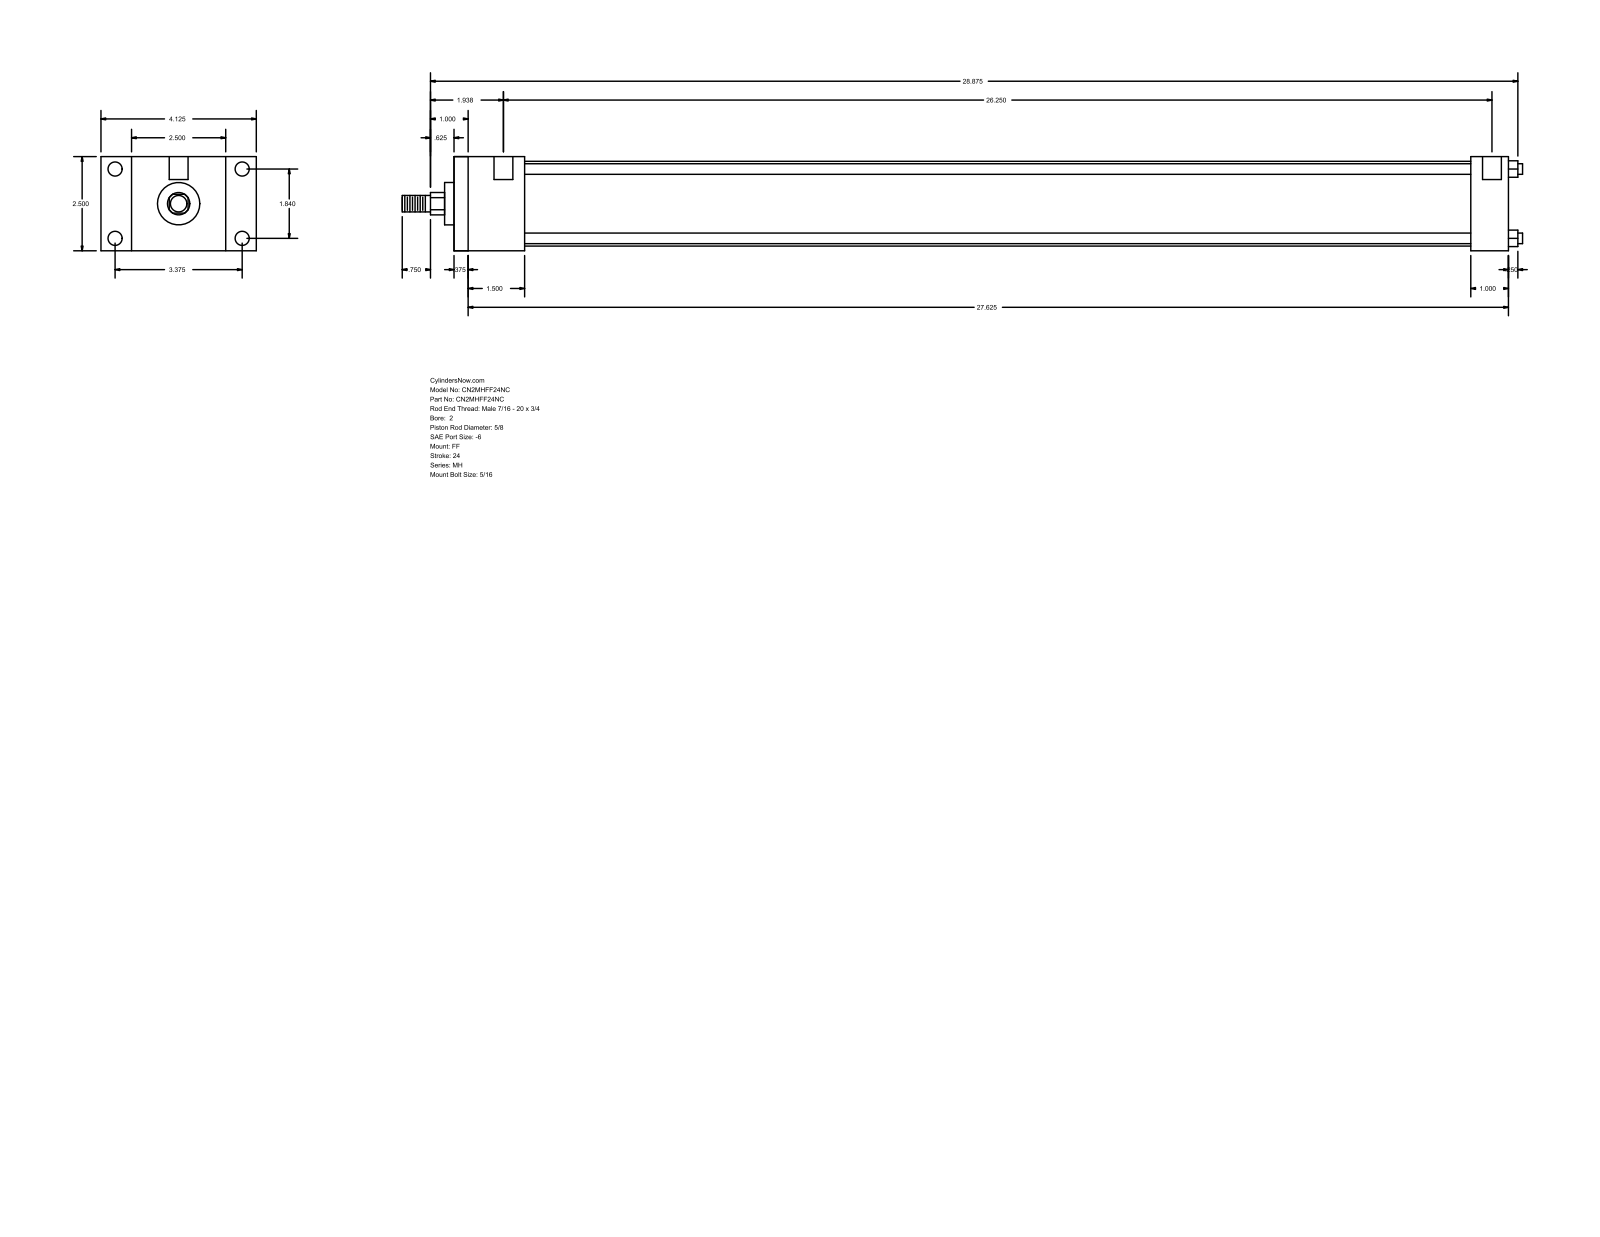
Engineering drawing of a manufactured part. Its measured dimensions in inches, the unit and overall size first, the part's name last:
Units: inches
Overall size (bounding box): 29.75 × 4.125 × 2.5
Round holes (diameter × count): ⌀0.219 ×4, ⌀0.375 ×4, ⌀0.5 ×2
Round bosses / shafts (diameter × count): ⌀0.281 ×4, ⌀2.25 ×1, ⌀1.125 ×1, ⌀0.625 ×1, ⌀0.437 ×1
Partial cylindrical surfaces — rounded edges, fillets, slot ends (radius × count): R0.297 ×1
Main face-to-face distances: 2.5, 28, 0.375, 27.625, 1.5, 1.875, 27, 26.625, 25.125, 26.125
Hole centre spacings: 1.84, 3.375, 3.844, 26.563, 0.125, 0.187, 26.25, 26.375
Bodies: 0 solids, 92 faces (64 planar, 28 cylindrical, 0 other)
Part name (STEP PRODUCT): MH_FF__0200_0.625
STEP written by: GSSL Pune (CONFIG_CONTROL_DESIGN)
